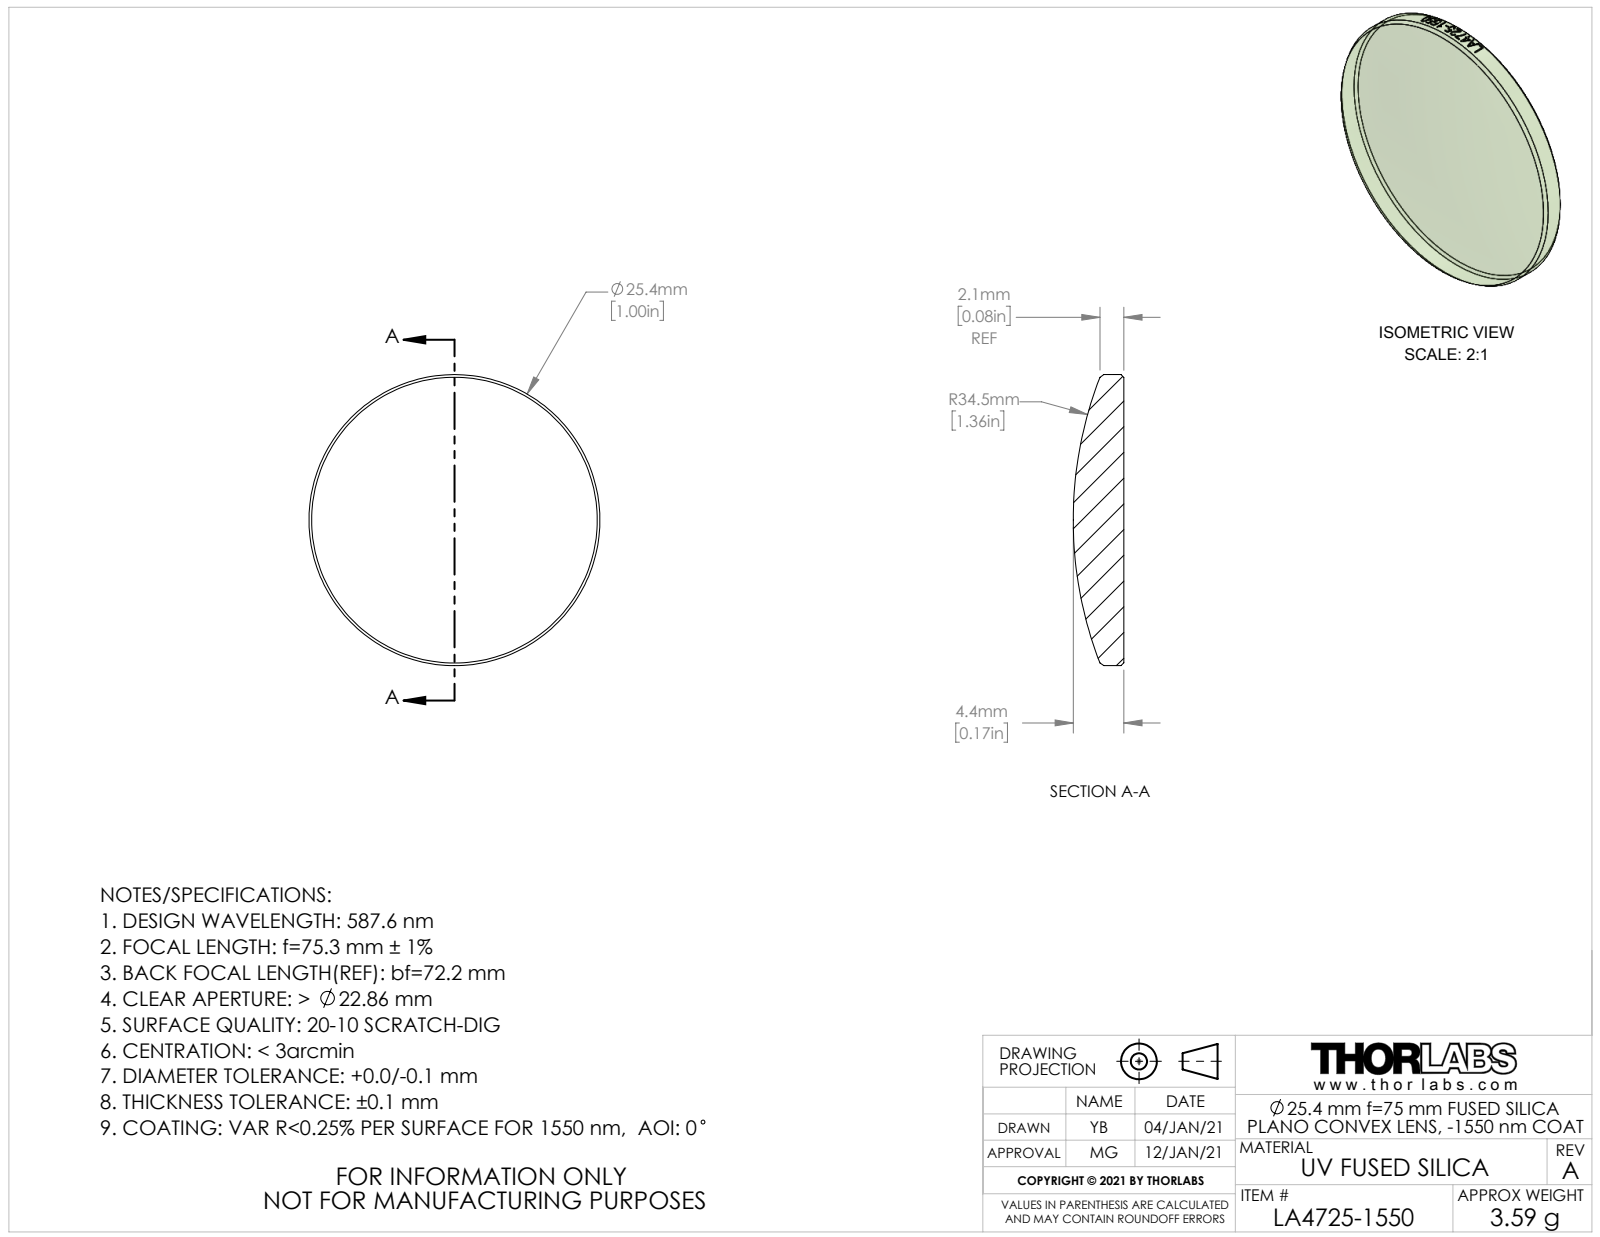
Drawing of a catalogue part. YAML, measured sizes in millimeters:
part_name: "CTN015944-E0W"
step_written_by: "SolidWorks 2018 (AUTOMOTIVE_DESIGN)"
units: millimeters
bodies: {solids: 1, faces: 26, planar: 1, cylindrical: 19, other: 6}
overall_size: [25.4, 25.4, 4.4]
volume: 1600
surface_area: 1173
round_bosses_or_shafts:
  - {diameter: 25.4, count: 1}
